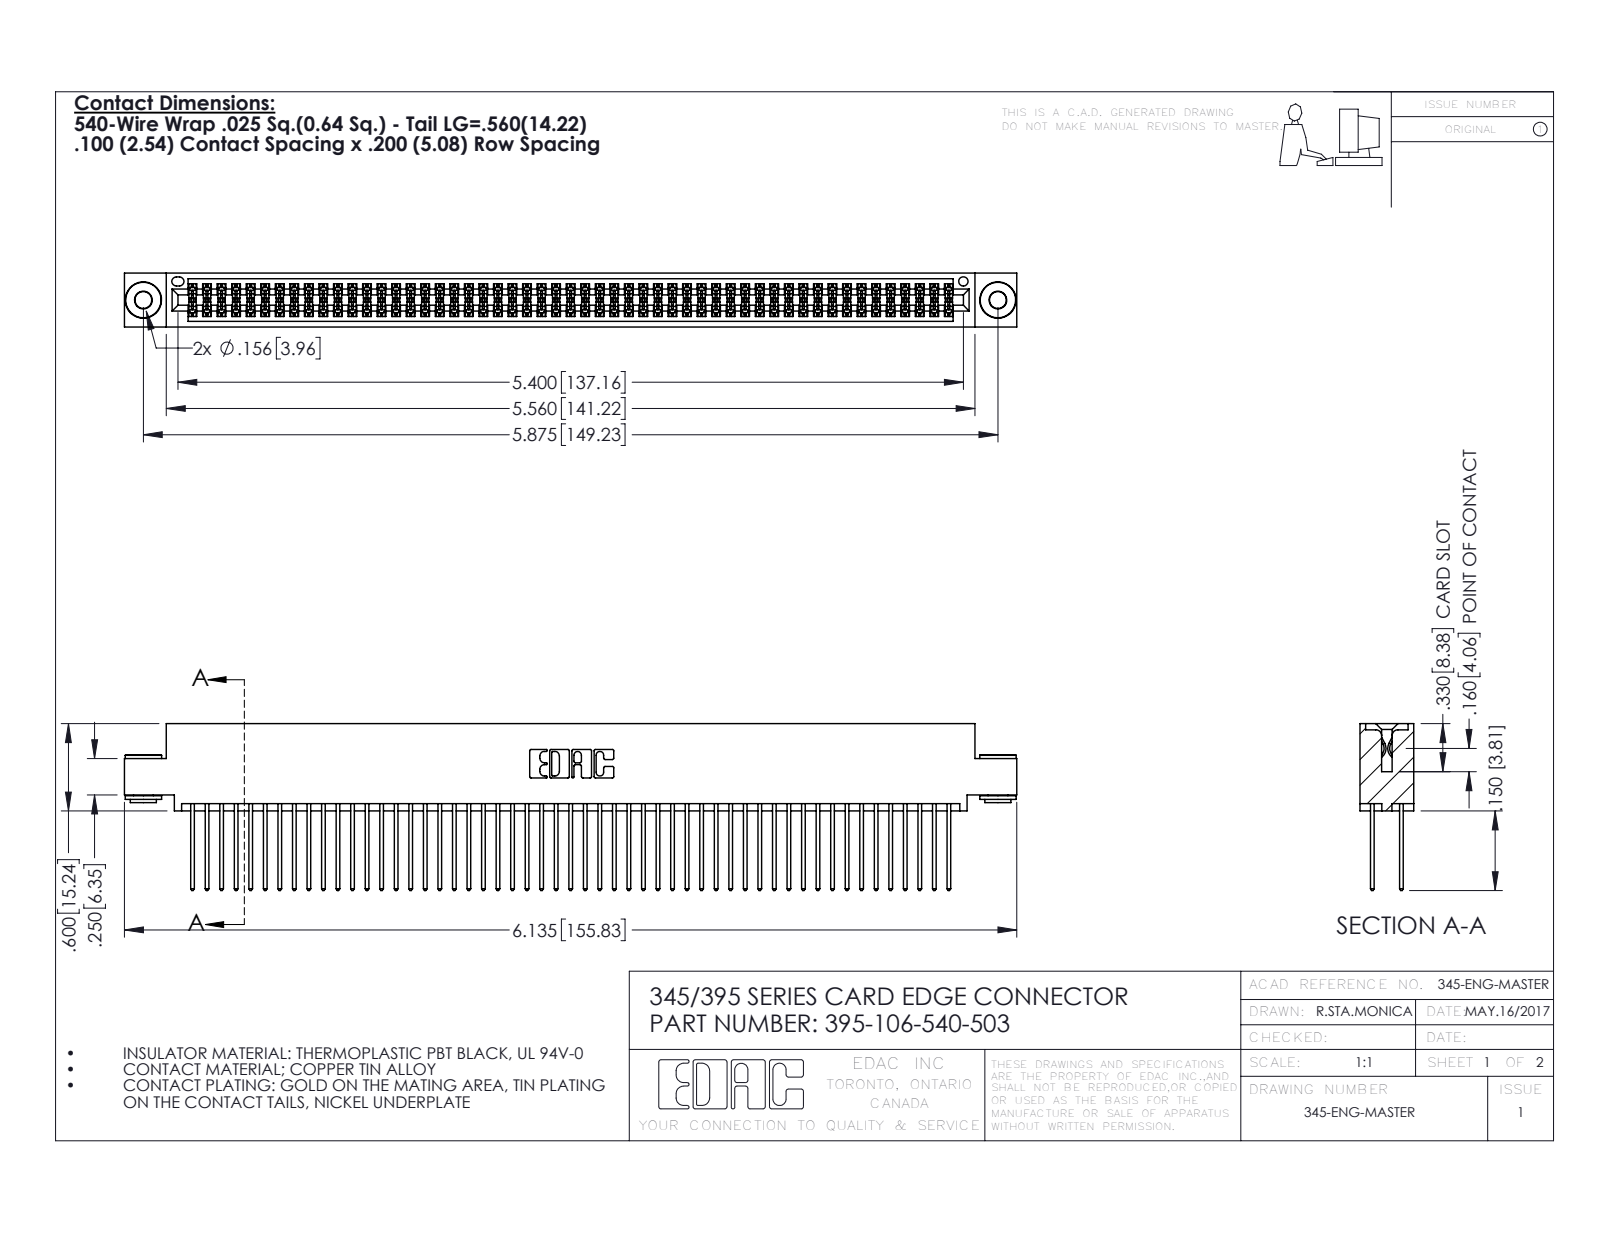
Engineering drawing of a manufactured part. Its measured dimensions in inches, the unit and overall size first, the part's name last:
Units: inches
Overall size (bounding box): 6.135 × 1.147 × 0.37
Round holes (diameter × count): ⌀0.116 ×2, ⌀0.156 ×2, ⌀0.064 ×1
Round bosses / shafts (diameter × count): ⌀0.25 ×2, ⌀0.18 ×2, ⌀0.136 ×2
Partial cylindrical surfaces — rounded edges, fillets, slot ends (radius × count): R0.006 ×159, R0.01 ×106, R0.01 ×22, R0.007 ×6, R0.031 ×6, R0.026 ×3, R0.014 ×2, R0.019 ×2
Main face-to-face distances: 0.072, 0.298, 0.2, 0.025, 0.098, 0.272, 0.37, 0.225, 0.175, 0.149
Hole centre spacings: 0.27, 5.639, 5.875
Volume: 0.951 in³ · Surface area: 39.39 in²
Bodies: 109 solids, 5468 faces (3592 planar, 1868 cylindrical, 8 other)
Part name (STEP PRODUCT): 345-292-001_345-293-140; 395-106-540-503; 345-250-002_345-250-002-102; 345 Part_0.110 Offset - 0.156 Dia-TH
STEP written by: SolidWorks 2016 (CONFIG_CONTROL_DESIGN)
